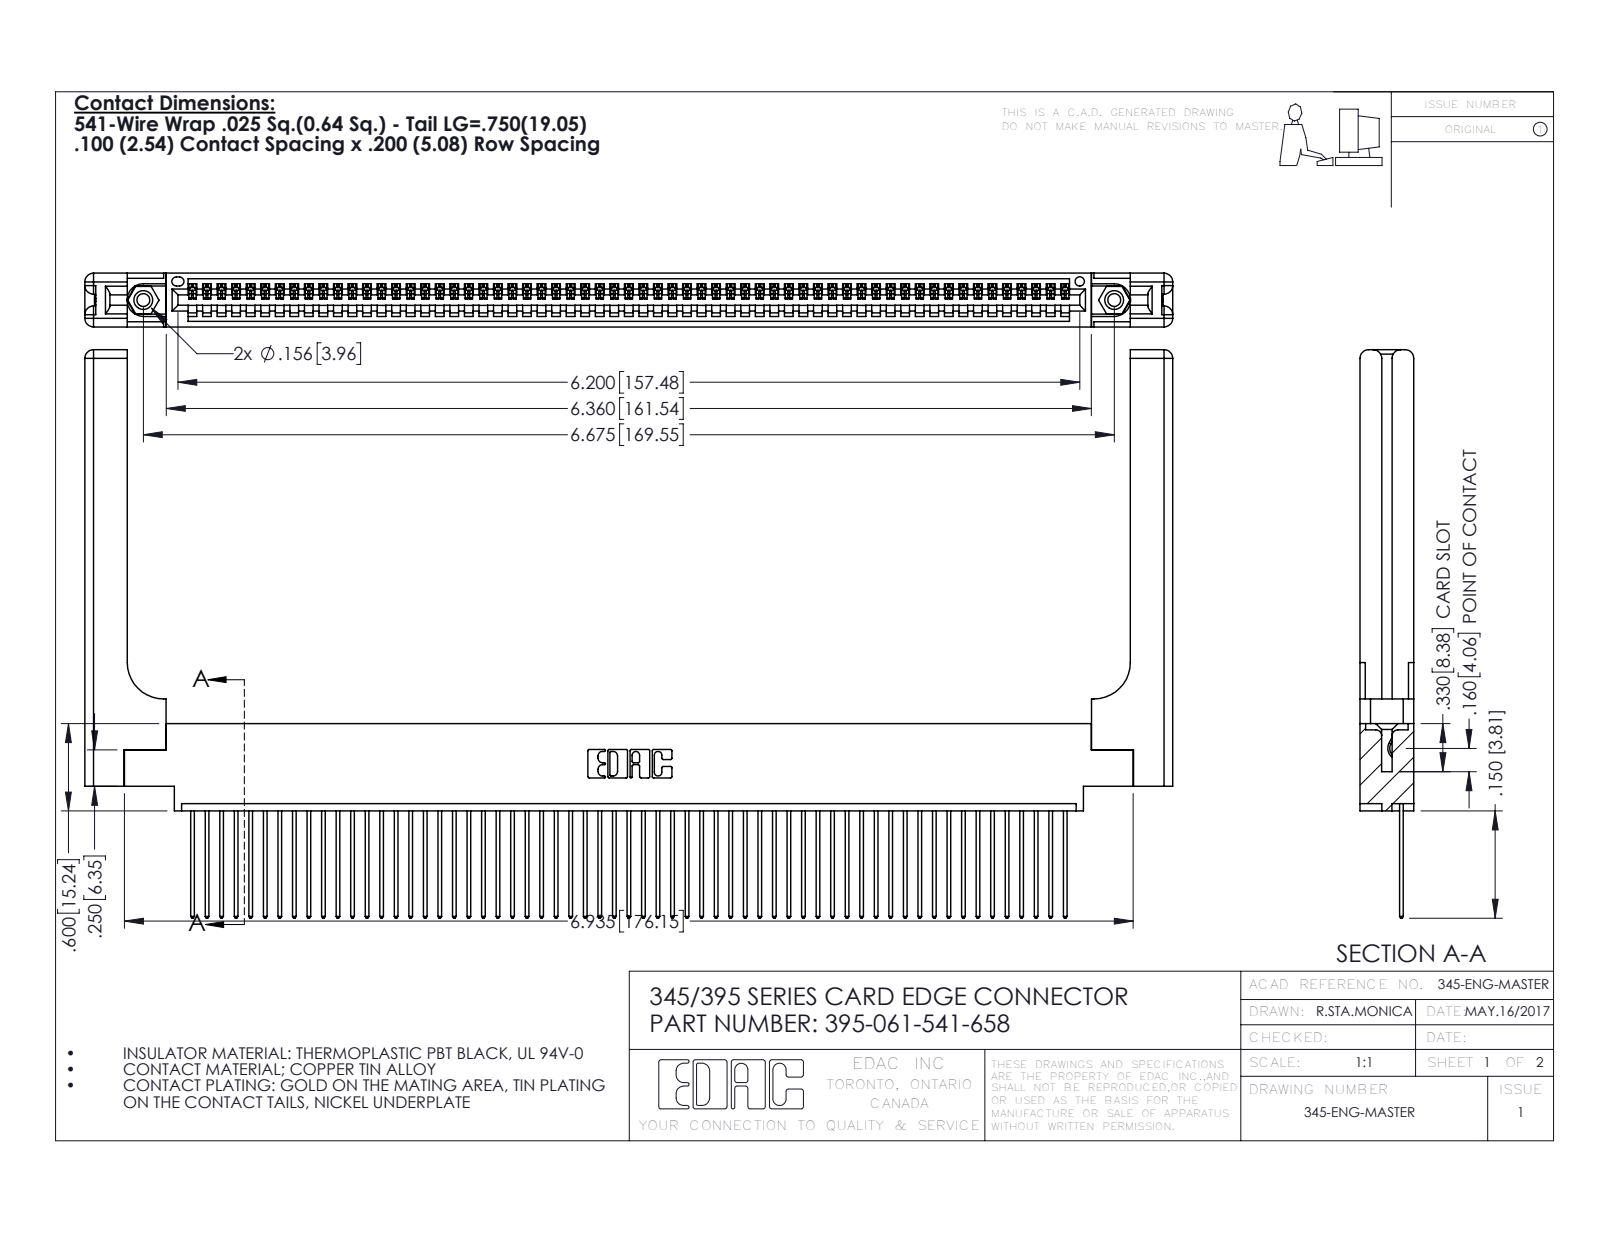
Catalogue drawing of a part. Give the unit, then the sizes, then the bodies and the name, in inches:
Units: inches
Overall size (bounding box): 7.479 × 3.907 × 0.37
Round holes (diameter × count): ⌀0.089 ×2, ⌀0.125 ×2, ⌀0.156 ×2, ⌀0.064 ×1
Round bosses / shafts (diameter × count): ⌀0.155 ×2
Partial cylindrical surfaces — rounded edges, fillets, slot ends (radius × count): R0.006 ×122, R0.01 ×122, R0.01 ×22, R0.06 ×16, R0.007 ×6, R0.031 ×6, R0.026 ×3, R0.03 ×2
Main face-to-face distances: 0.072, 0.298, 0.37, 0.098, 0.272, 0.025, 0.2, 0.225, 0.148, 0.15
Hole centre spacings: 0.27, 6.439, 6.675
Volume: 1.635 in³ · Surface area: 48.32 in²
Bodies: 66 solids, 3924 faces (2672 planar, 1192 cylindrical, 60 other)
Part name (STEP PRODUCT): 345-250-001_345-250-001-102; 345-220-058_345-220-058; 395-061-541-658; 345 Part_0.170 Offset - 0.156 Dia-TH (+1 more)
STEP written by: SolidWorks 2016 (CONFIG_CONTROL_DESIGN)
